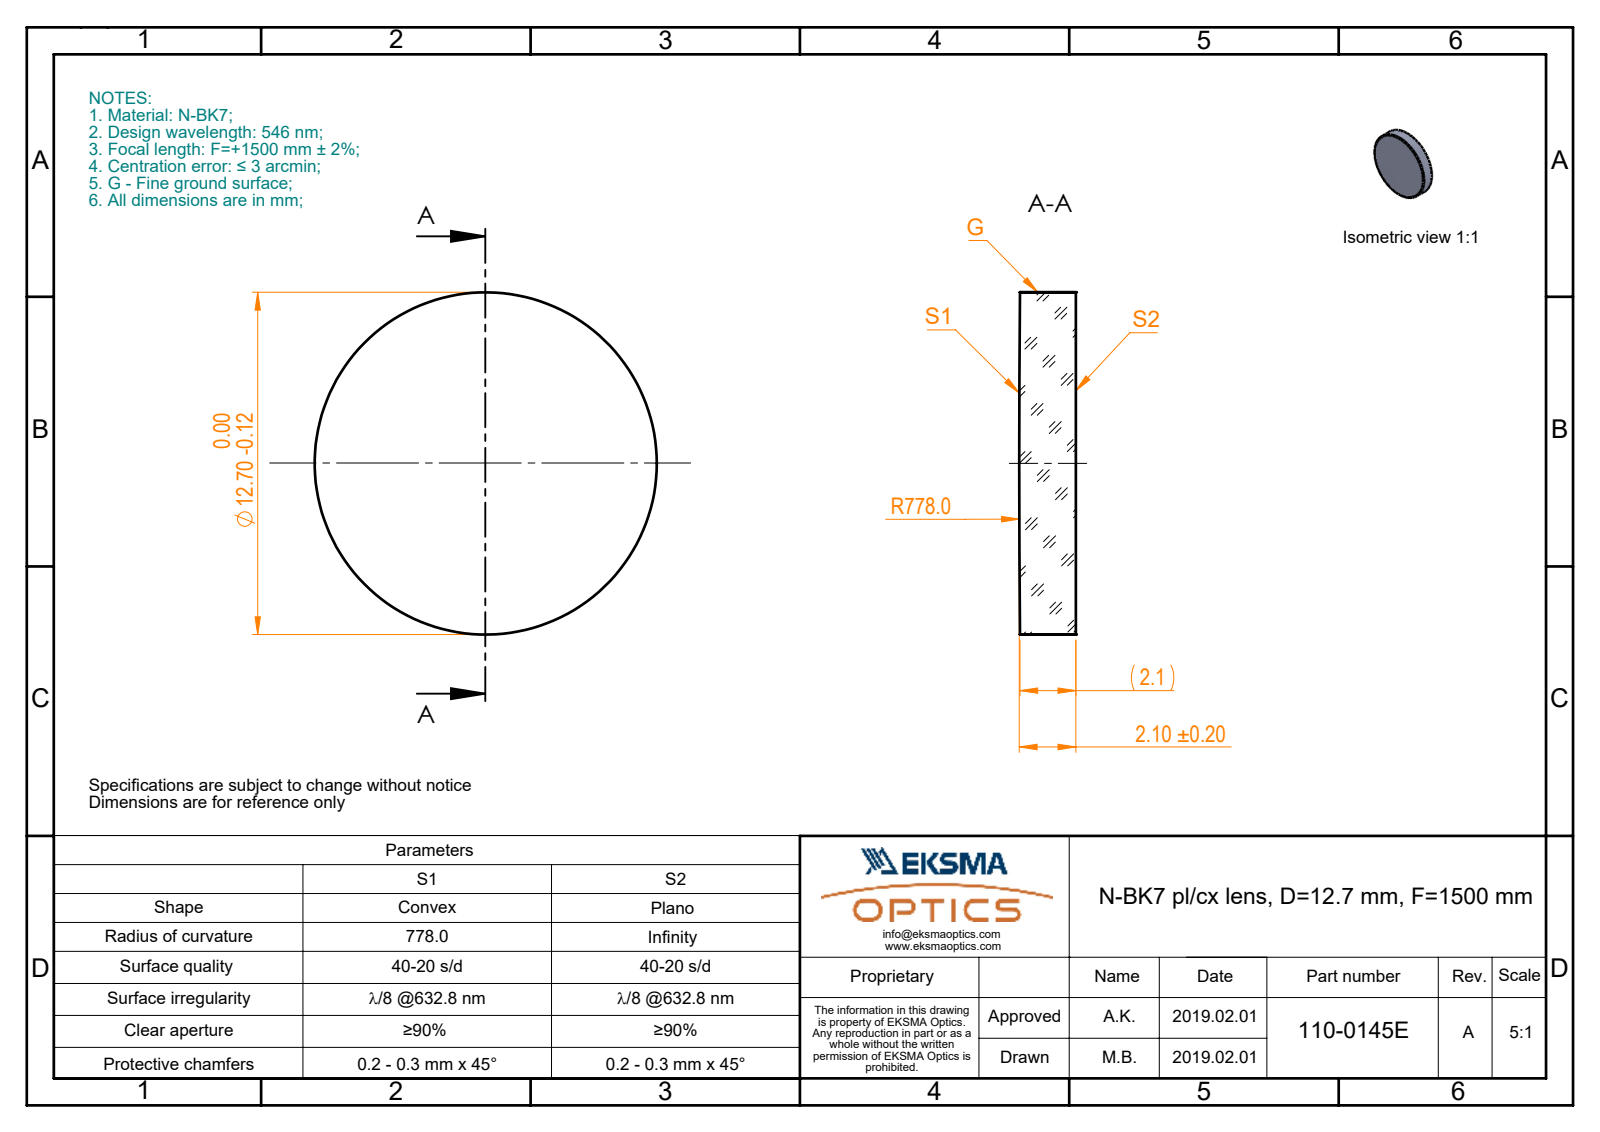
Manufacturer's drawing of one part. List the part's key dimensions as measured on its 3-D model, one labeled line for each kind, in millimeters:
Part name (STEP PRODUCT): 110-0145E BK7 pl-cx 12.7 F1500
STEP written by: SolidWorks 2017 (CONFIG_CONTROL_DESIGN)
Units: millimetres
Bodies: 1 solid, 5 faces (1 planar, 2 cylindrical, 2 other)
Overall size (bounding box): 12.7 × 12.7 × 2.1
Volume: 264 mm³ · Surface area: 336 mm²
Round bosses / shafts (diameter × count): ⌀12.7 ×1
